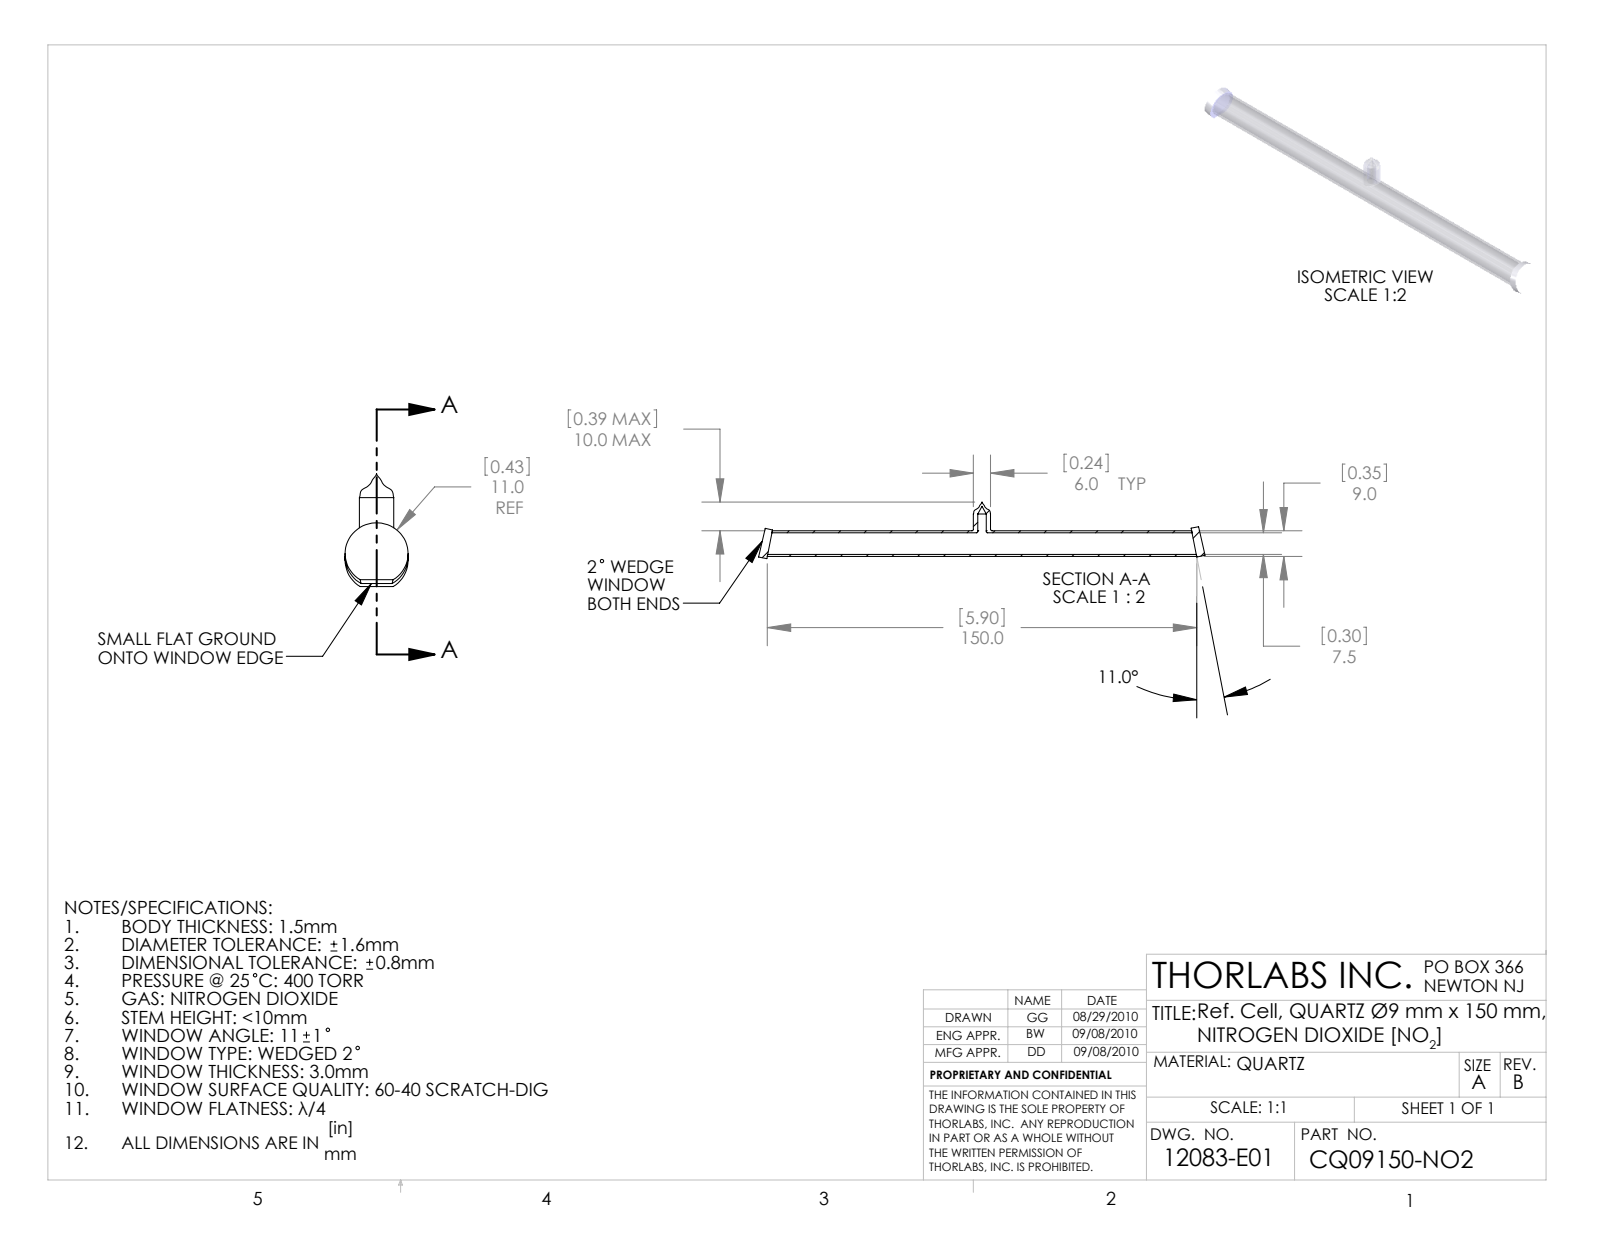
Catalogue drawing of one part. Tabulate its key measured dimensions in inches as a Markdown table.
| quantity | value |
| --- | --- |
| part name | 12083-E0W |
| STEP written by | SolidWorks 2009 (AUTOMOTIVE_DESIGN) |
| units | inches |
| bodies | 3 solids, 33 faces (8 planar, 17 cylindrical, 8 other) |
| overall size | 6.14 × 0.777 × 0.433 |
| volume | 0.217 in³ |
| surface area | 13.17 in² |
| round holes (diameter × count) | 0.115 × 1, 0.118 × 1, 0.295 × 1 |
| round bosses / shafts (diameter × count) | 0.433 × 2, 0.354 × 1, 0.236 × 1 |
